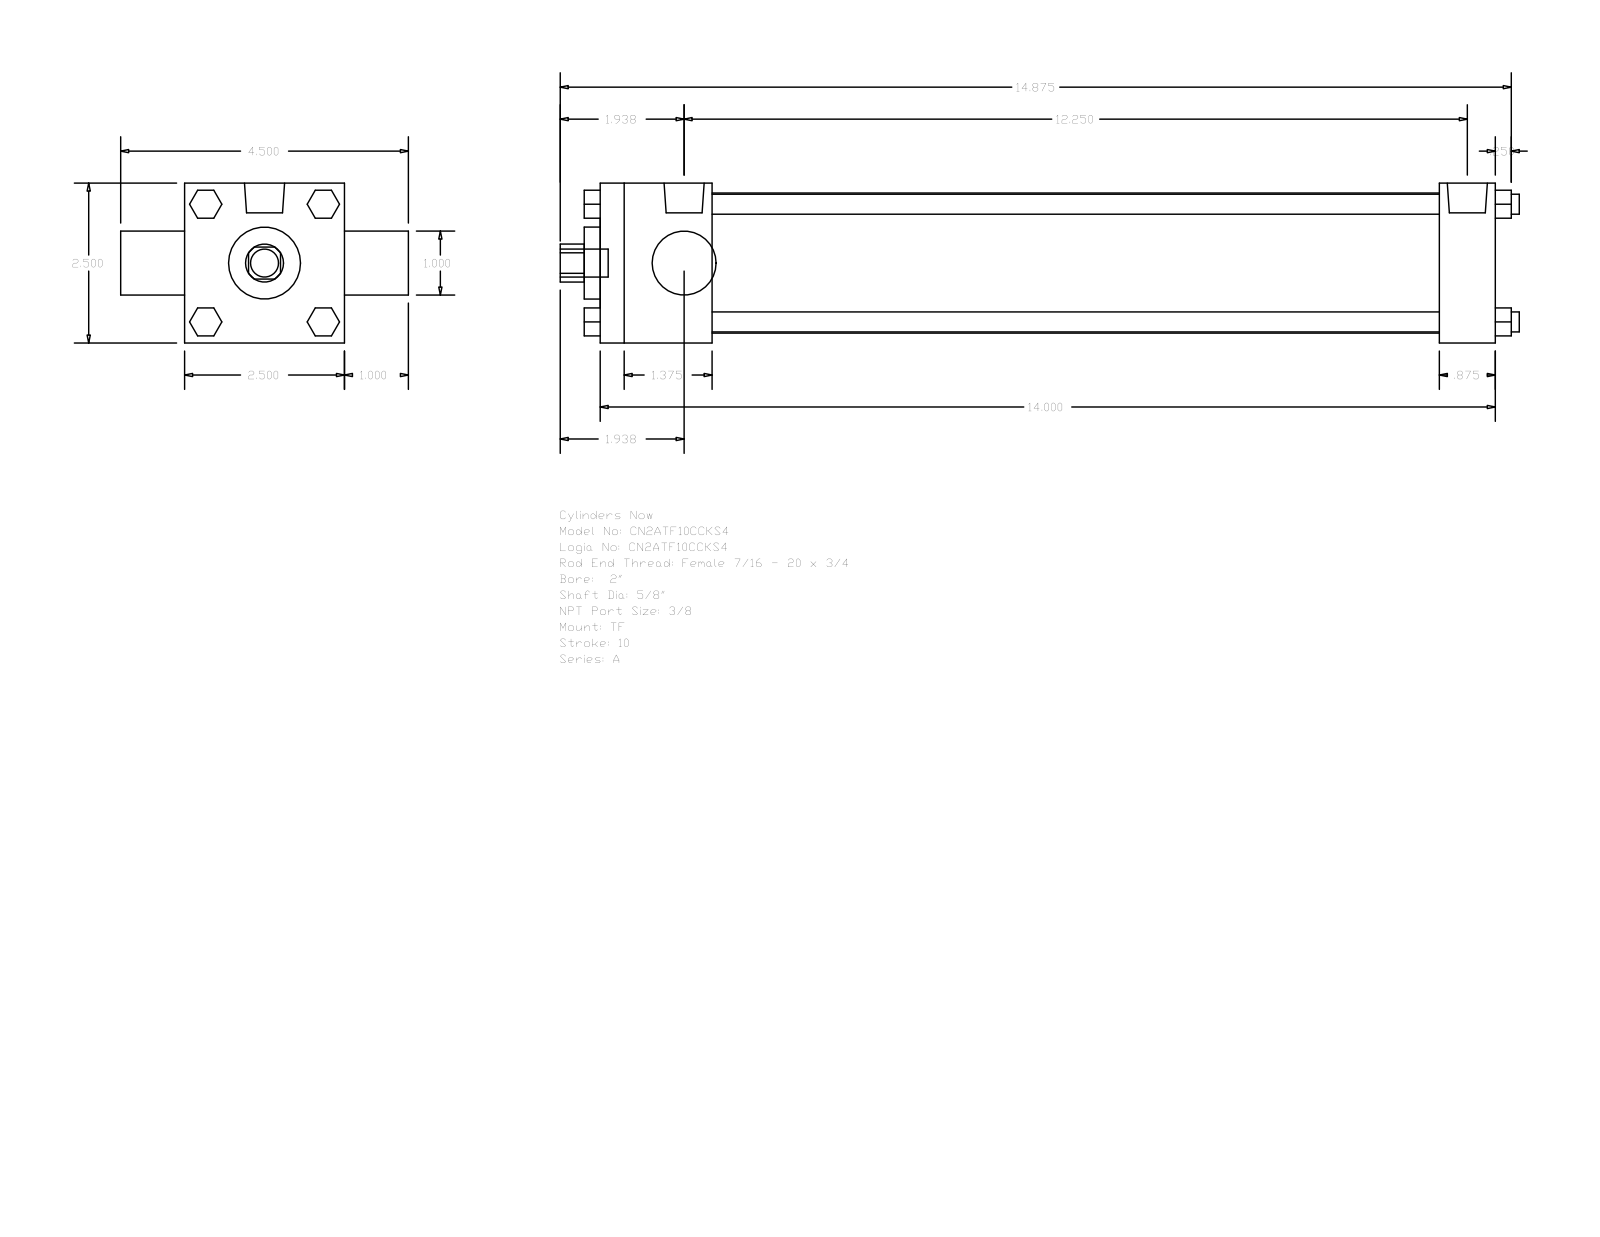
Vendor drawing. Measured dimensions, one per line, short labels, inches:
name: A_TF__0200_0.625
written by: GSSL Pune (CONFIG_CONTROL_DESIGN)
unit: in
bodies: 0 solids, 120 faces (92 planar, 28 cylindrical, 0 other)
size: 15 × 4.5 × 2.5
holes: 1× ⌀0.625, 1× ⌀1, 1× ⌀1.125, 1× ⌀2.19
bosses: 4× ⌀0.313, 3× ⌀0.219, 2× ⌀0.627, 1× ⌀0.437
rounds: 1× R0.297
face distances: 2.5, 14, 1.75, 13.125, 11.375, 12.25, 0.875, 1, 3.5, 2
